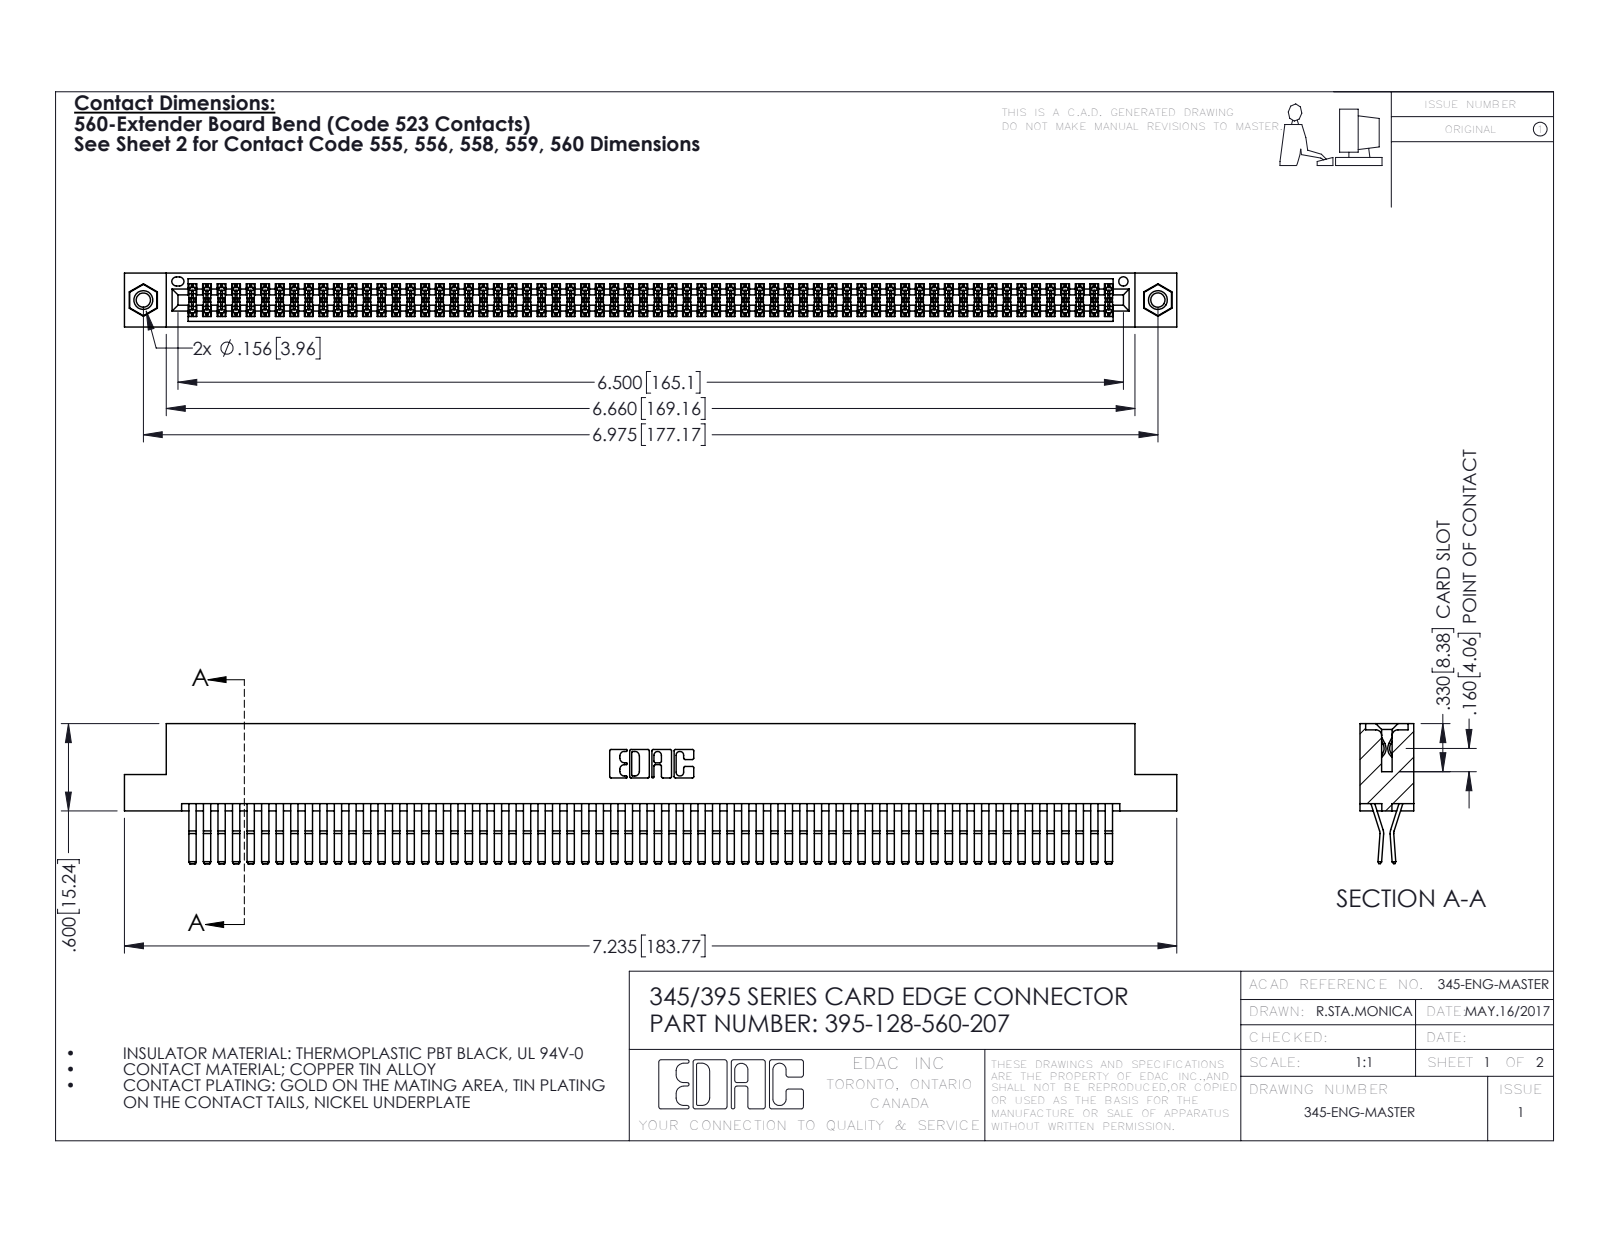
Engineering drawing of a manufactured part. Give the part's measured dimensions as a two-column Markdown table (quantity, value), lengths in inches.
| quantity | value |
| --- | --- |
| part name | 345-292-001_560 Tail; 345-250-001_345-250-005-103; 345 Part_Flush Mounting Lugs - 0.156 Dia-TI; 395-128-560-207 |
| STEP written by | SolidWorks 2016 (CONFIG_CONTROL_DESIGN) |
| units | inches |
| bodies | 131 solids, 6842 faces (4336 planar, 2490 cylindrical, 16 other) |
| overall size | 7.235 × 0.962 × 0.37 |
| volume | 1.152 in³ |
| surface area | 47.31 in² |
| round holes (diameter × count) | 0.098 × 2, 0.125 × 2, 0.156 × 2, 0.064 × 1 |
| round bosses / shafts (diameter × count) | 0.155 × 2 |
| partial cylindrical surfaces (radius × count) | 0.006 × 192, 0.01 × 22, 0.007 × 6, 0.031 × 6, 0.026 × 3, 0.01 × 2, 0.014 × 2, 0.019 × 2 |
| main face-to-face distances | 0.025, 0.072, 0.298, 0.37, 0.2, 0.098, 0.272, 0.225, 0.175, 0.149 |
| hole center spacings | 0.27, 6.739, 6.975 |
